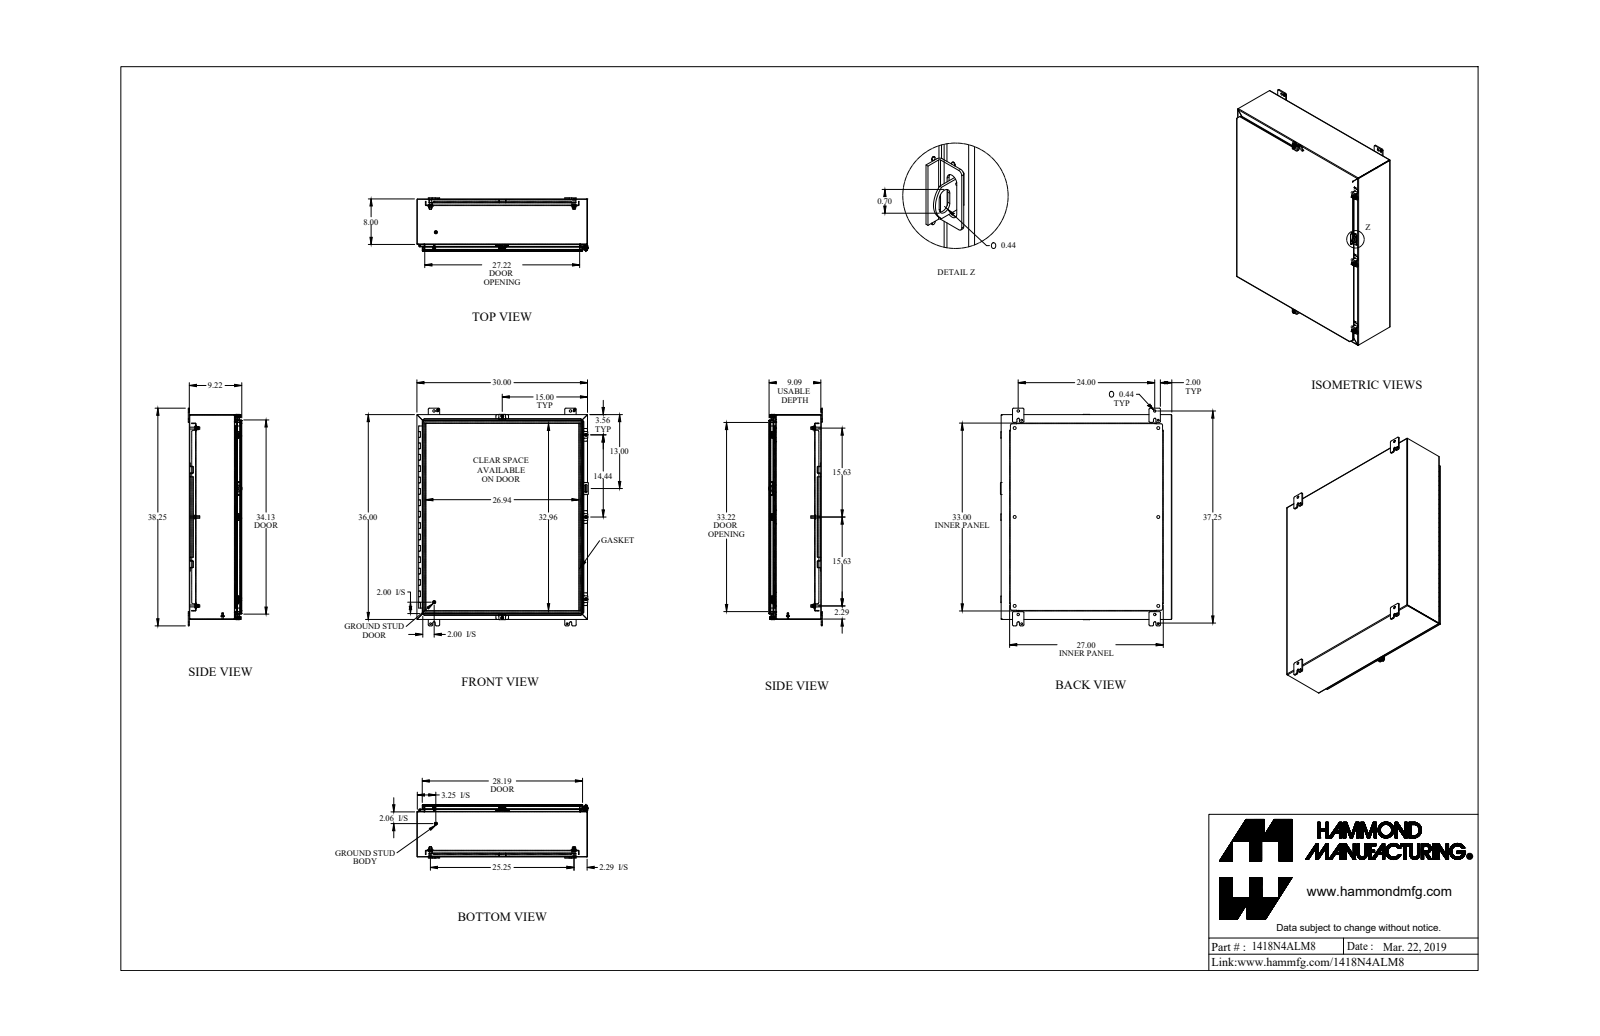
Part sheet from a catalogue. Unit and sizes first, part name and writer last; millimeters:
Units: millimetres
Overall size (bounding box): 971.6 × 765.2 × 239.7
Round holes (diameter × count): ⌀12.7 ×6, ⌀5.9 ×5, ⌀6.7 ×5, ⌀9.5 ×5, ⌀7.8 ×4, ⌀8 ×4, ⌀11.1 ×4, ⌀11.3 ×4, ⌀3.2 ×1, ⌀4.7 ×1, ⌀88.9 ×1
Round bosses / shafts (diameter × count): ⌀3.3 ×14, ⌀16.5 ×6, ⌀9.5 ×6, ⌀8.4 ×6, ⌀12.7 ×5, ⌀10.2 ×5, ⌀6.2 ×5, ⌀25.4 ×4
Partial cylindrical surfaces — rounded edges, fillets, slot ends (radius × count): R6.4 ×52, R1.3 ×30, R3.8 ×30, R4.8 ×24, R1 ×15, R3.1 ×15, R1 ×14, R3.1 ×14
Main face-to-face distances: 2.1, 2.5, 229.6, 231.7, 2.4, 232.2, 234.2, 204.4, 201.8, 27.8
Hole centre spacings: 641.4, 396.9, 609.6, 754.2, 1093.7, 61.8, 696, 800.6
Volume: 7 237 000 mm³ · Surface area: 6 513 000 mm²
Bodies: 54 solids, 2123 faces (1254 planar, 737 cylindrical, 132 other)
Part name (STEP PRODUCT): 1418N4ALM8_Default
STEP written by: SolidWorks 2019 (CONFIG_CONTROL_DESIGN)
